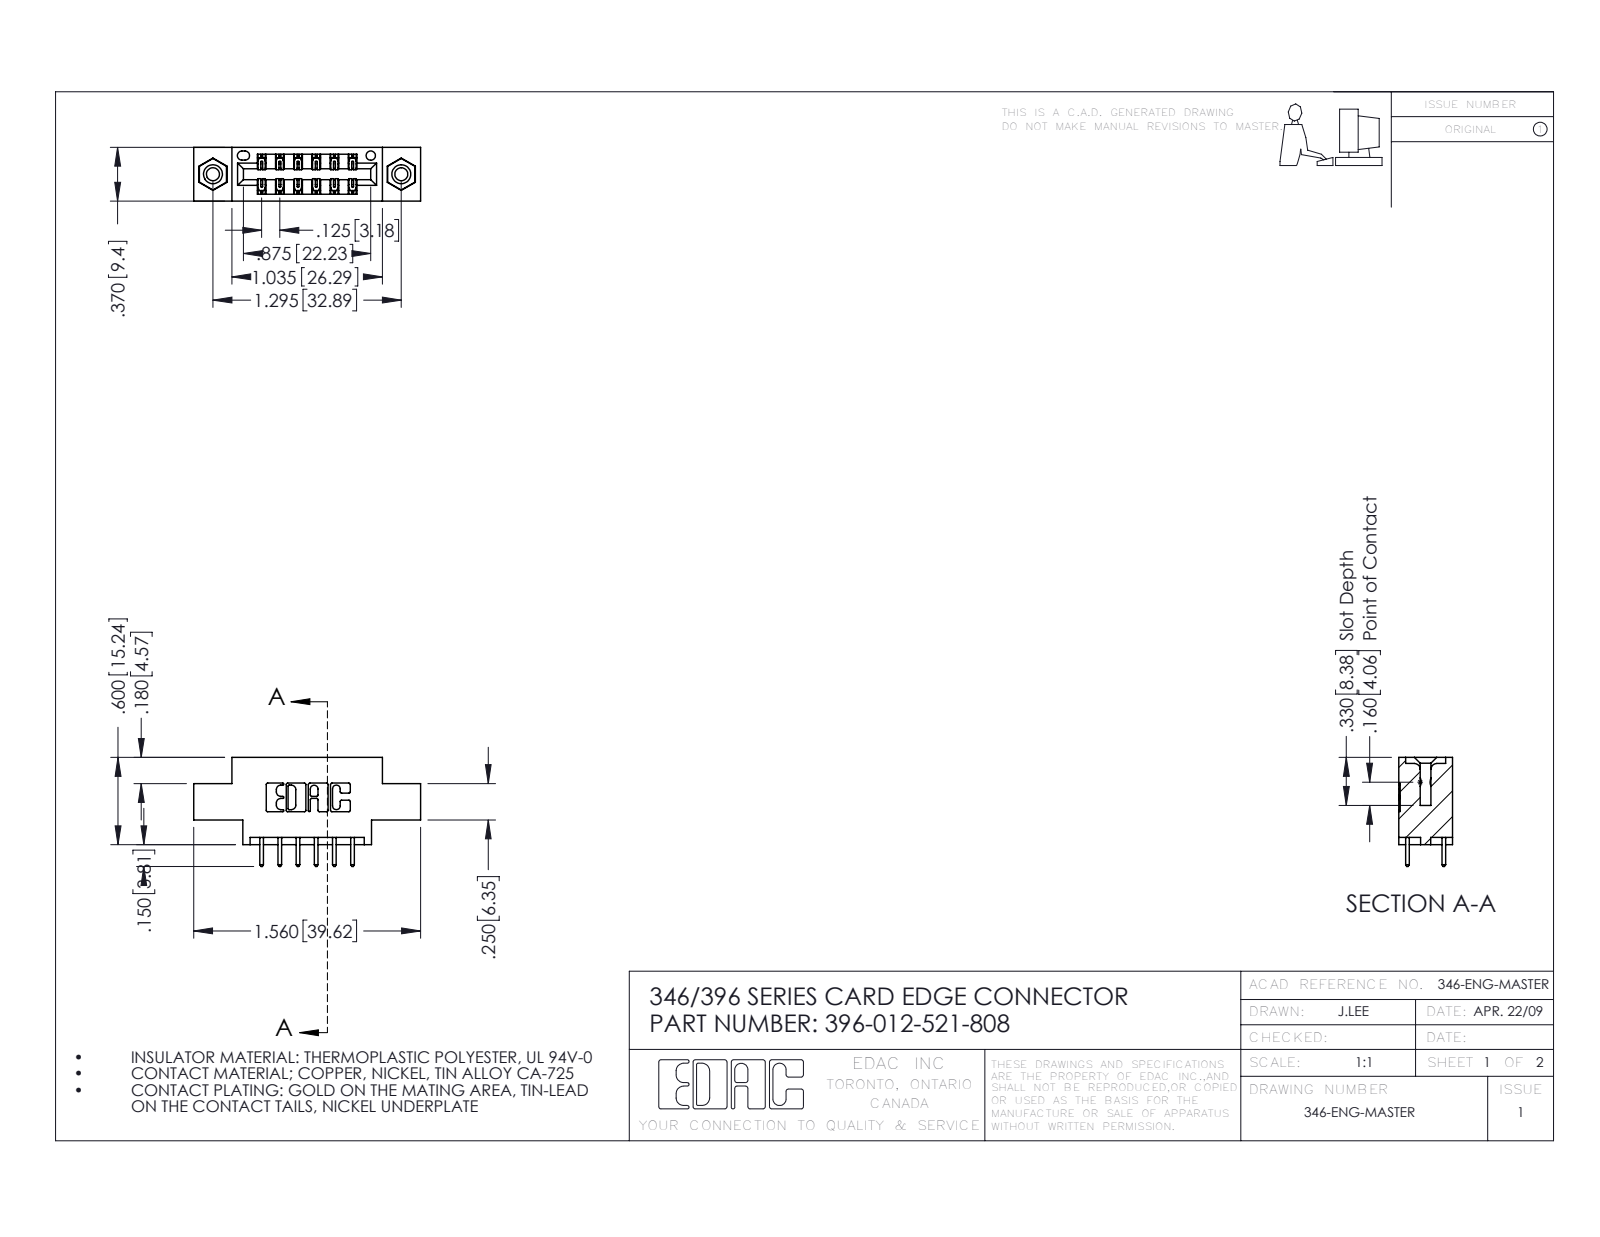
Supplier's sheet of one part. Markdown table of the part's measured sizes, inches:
| quantity | value |
| --- | --- |
| part name | 346 Part_0.170 Offset - 0.156 Dia-TI; 345-292-001_345-293-121; 396-012-521-808; 345-250-001_345-250-003-102 |
| STEP written by | SolidWorks 2016 (CONFIG_CONTROL_DESIGN) |
| units | inches |
| bodies | 15 solids, 810 faces (532 planar, 262 cylindrical, 16 other) |
| overall size | 1.56 × 0.75 × 0.37 |
| volume | 0.209 in³ |
| surface area | 6.664 in² |
| round holes (diameter × count) | 0.089 × 2, 0.125 × 2, 0.156 × 2, 0.064 × 1 |
| round bosses / shafts (diameter × count) | 0.155 × 2 |
| partial cylindrical surfaces (radius × count) | 0.01 × 22, 0.006 × 18, 0.01 × 12, 0.007 × 6, 0.031 × 6, 0.026 × 3, 0.014 × 2, 0.022 × 2 |
| main face-to-face distances | 0.25, 0.37, 0.048, 0.322, 0.222, 0.148, 0.072, 0.298, 0.025, 0.1 |
| hole center spacings | 0.246, 1.092, 1.295 |
